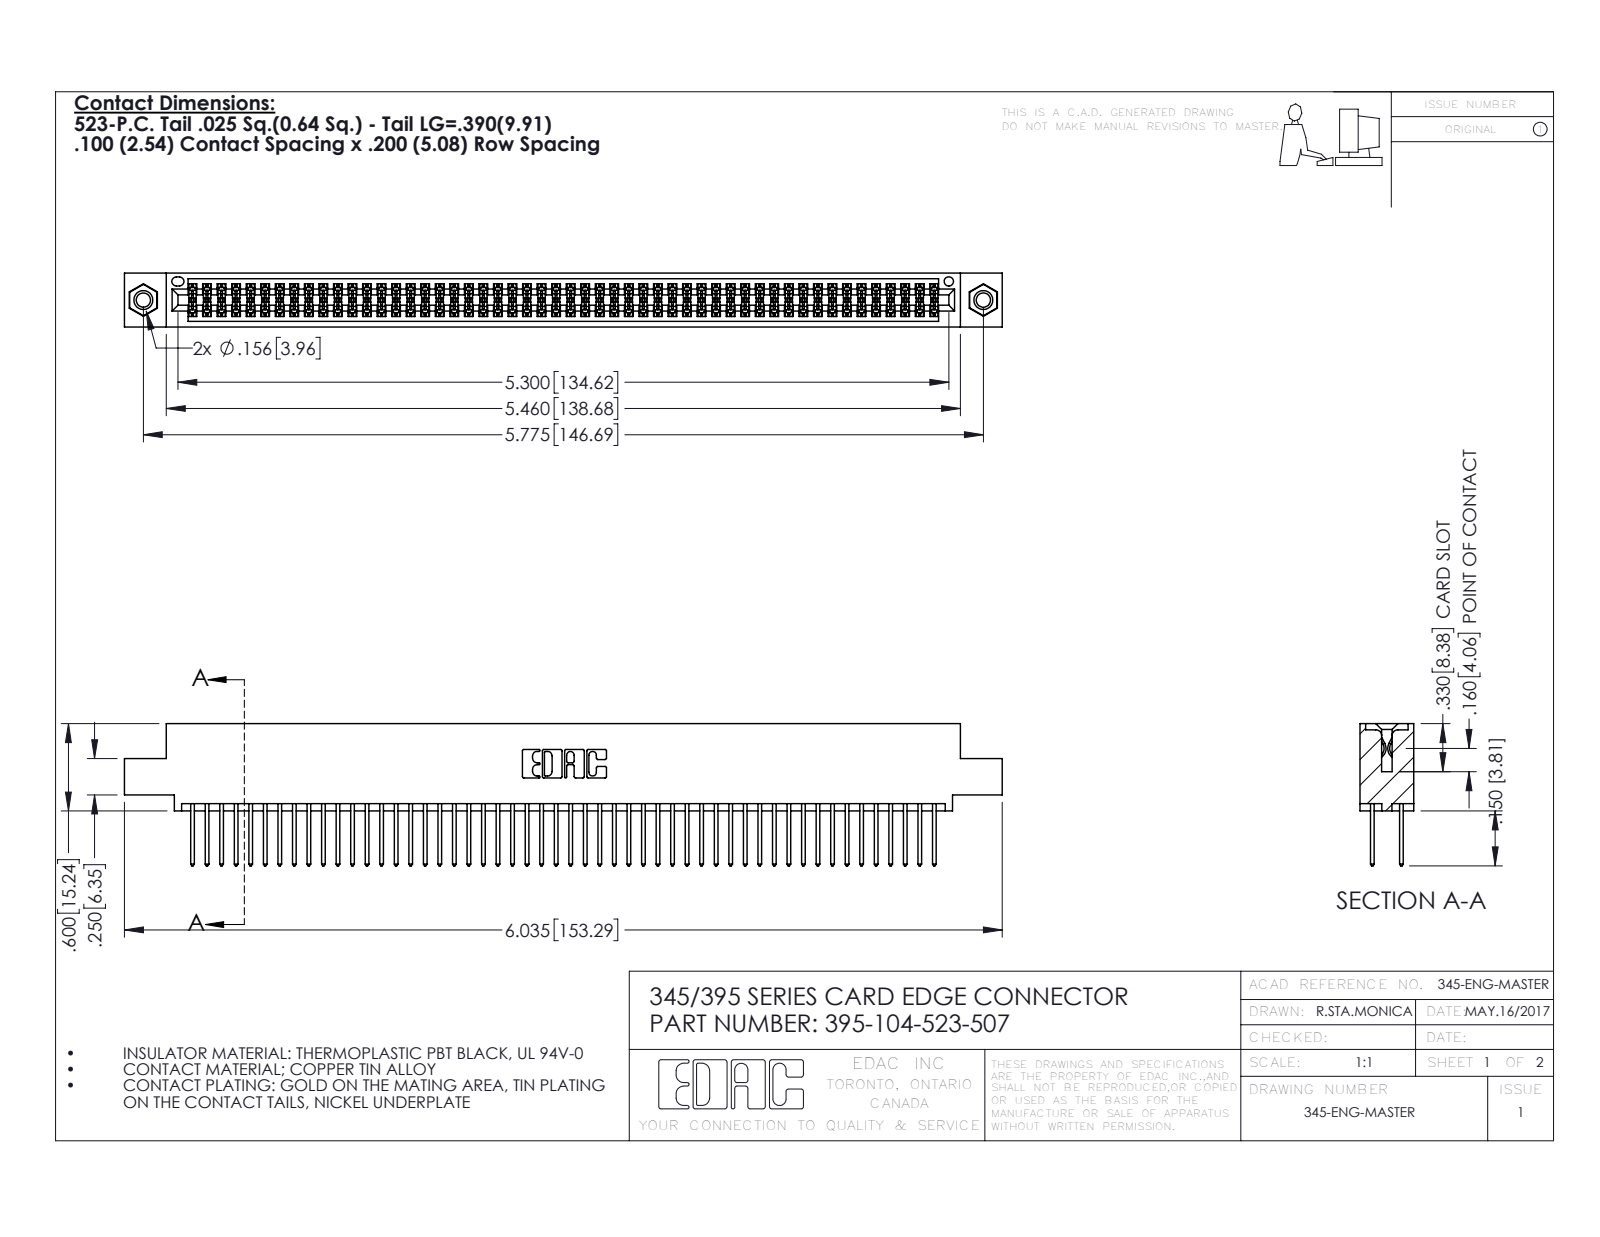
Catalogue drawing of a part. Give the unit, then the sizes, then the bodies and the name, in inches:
Units: inches
Overall size (bounding box): 6.035 × 0.977 × 0.37
Round holes (diameter × count): ⌀0.098 ×2, ⌀0.125 ×2, ⌀0.156 ×2, ⌀0.064 ×1
Round bosses / shafts (diameter × count): ⌀0.155 ×2
Partial cylindrical surfaces — rounded edges, fillets, slot ends (radius × count): R0.006 ×156, R0.01 ×104, R0.01 ×22, R0.007 ×6, R0.031 ×6, R0.026 ×3, R0.014 ×2, R0.019 ×2
Main face-to-face distances: 0.072, 0.298, 0.2, 0.098, 0.272, 0.025, 0.37, 0.225, 0.175, 0.149
Hole centre spacings: 0.27, 5.539, 5.775
Volume: 0.922 in³ · Surface area: 36.59 in²
Bodies: 107 solids, 5390 faces (3548 planar, 1826 cylindrical, 16 other)
Part name (STEP PRODUCT): 345 Part_0.110 Offset - 0.156 Dia-TI; 345-292-001_345-293-123; 345-250-001_345-250-005-103; 395-104-523-507
STEP written by: SolidWorks 2016 (CONFIG_CONTROL_DESIGN)
